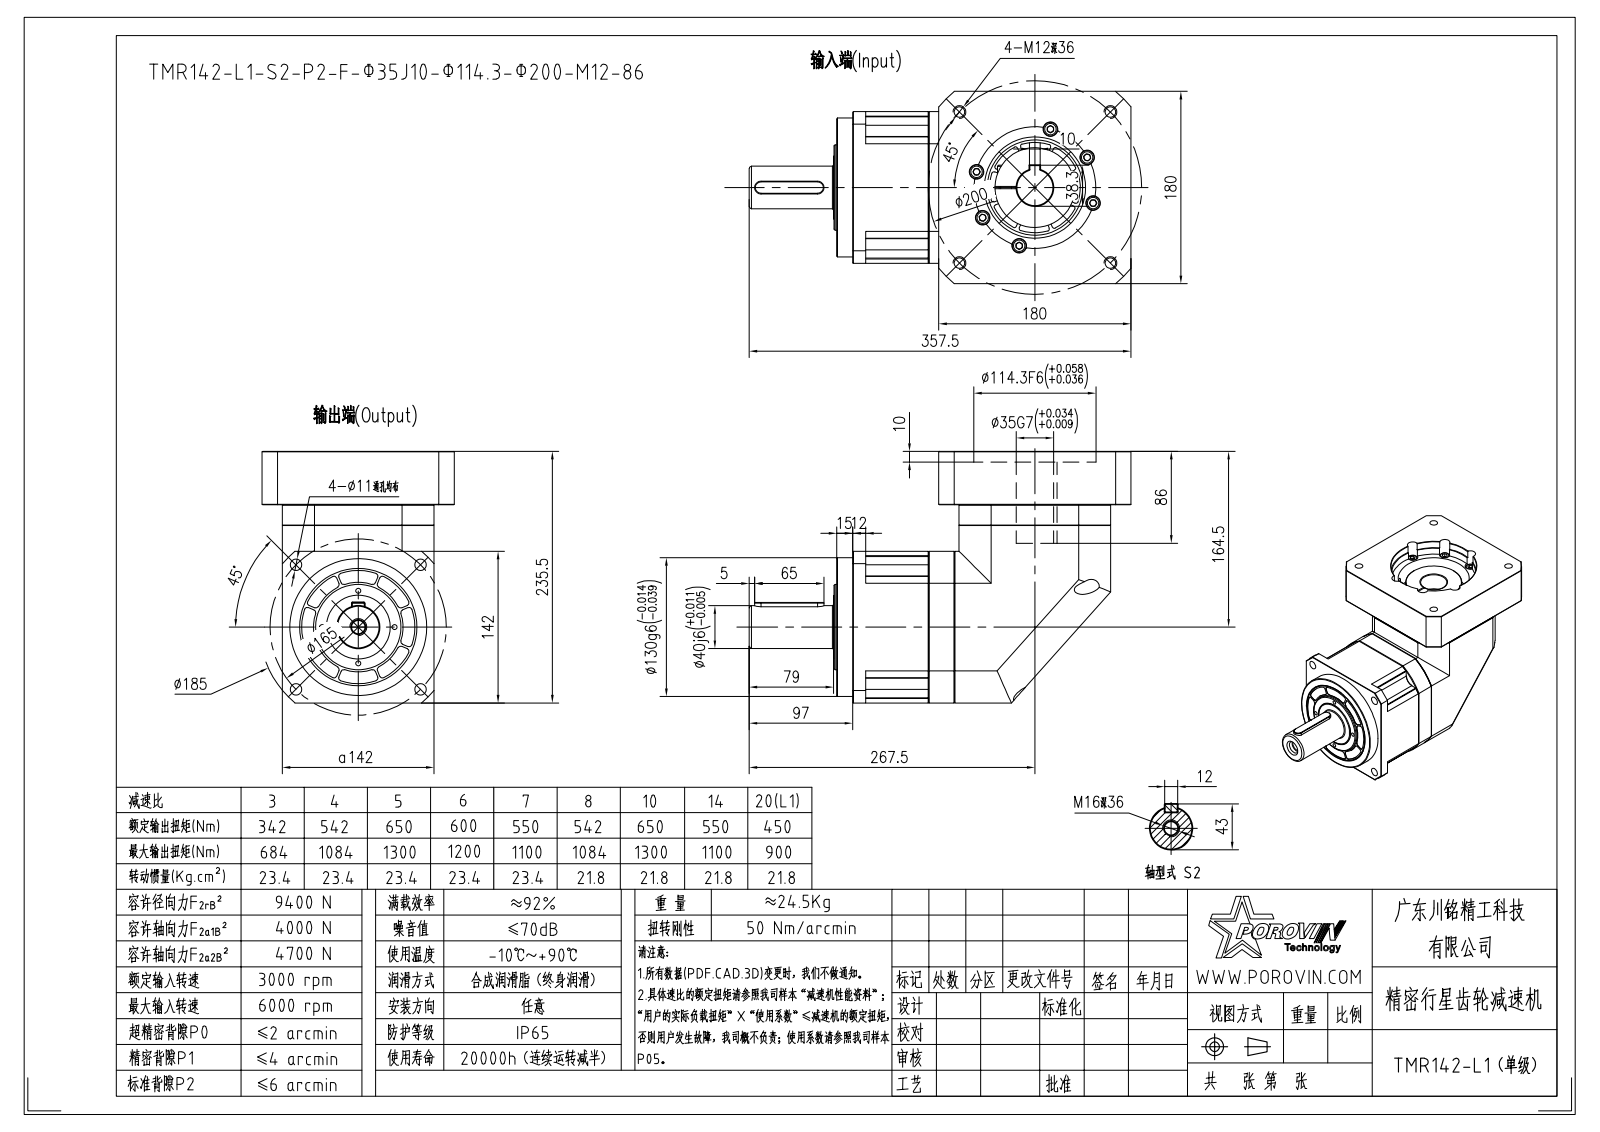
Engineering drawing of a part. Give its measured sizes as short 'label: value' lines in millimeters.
name: HEXAGON_SOCKET_HEAD_CAP_S-16694; SPRING_LOCK_WASHERS--NORMAL_TYP; HEX_SOCKET_SET_SCREWS_WITH_FLAT; TMR1420001 (+8 more)
written by: CREO PARAMETRIC BY PTC INC, 2020053 (CONFIG_CONTROL_DESIGN)
unit: mm
bodies: 42 solids, 1360 faces (536 planar, 557 cylindrical, 267 other)
size: 357.5 × 235.5 × 180
volume: 6 065 000 mm³; area: 540 465 mm²
holes: 16× ⌀8.68, 16× ⌀9, 16× ⌀14, 13× ⌀6.8, 4× ⌀5, 4× ⌀10.2, 4× ⌀11, 1× ⌀8.5, 1× ⌀10.5, 1× ⌀13.6, 1× ⌀17, 1× ⌀17.5
bosses: 16× ⌀13, 16× ⌀12.88, 16× ⌀8, 1× ⌀130, 1× ⌀125, 1× ⌀80, 1× ⌀75, 1× ⌀67
rounds: 64× R2, 20× R1, 4× R10.5, 3× R6, 3× R82, 2× R42.5, 1× R8.25, 1× R50
face distances: 142, 24.3, 24.5, 19, 19.5, 161, 50, 69.5, 180, 3
hole spacings: 56.5, 43.24, 62.84, 79.9, 104.39, 110.07, 21.17, 46.62
